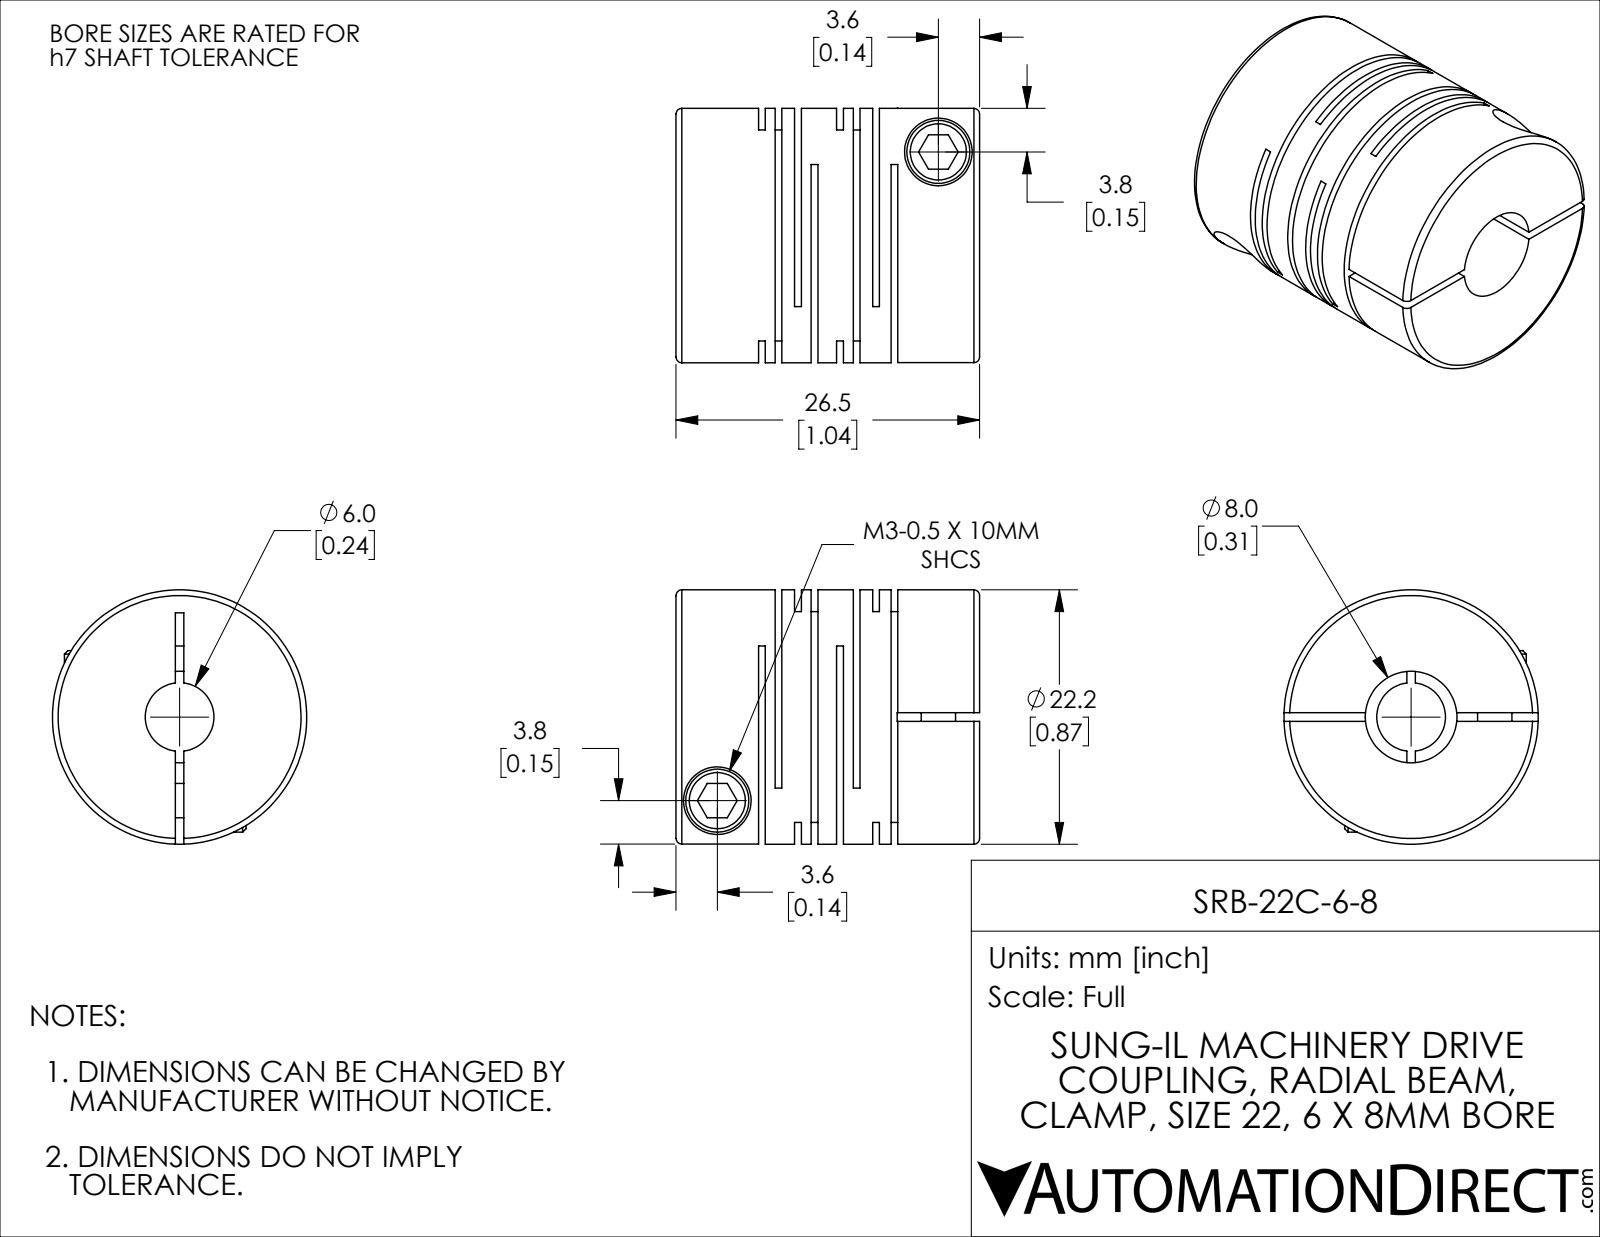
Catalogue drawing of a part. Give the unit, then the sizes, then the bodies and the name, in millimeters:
Units: millimetres
Overall size (bounding box): 26.5 × 22.2 × 22.2
Round holes (diameter × count): ⌀3 ×2, ⌀5.9 ×2, ⌀6 ×1, ⌀8 ×1
Round bosses / shafts (diameter × count): ⌀5.5 ×2, ⌀22.2 ×1
Main face-to-face distances: 0.59, 6.82, 1.45, 3.15, 5.37, 1.7, 3.67, 2.04, 7.41, 6.23
Volume: 7 458 mm³ · Surface area: 7 884 mm²
Bodies: 1 solid, 115 faces (60 planar, 42 cylindrical, 13 other)
Part name (STEP PRODUCT): SRB-22C-6-8
STEP written by: SolidWorks 2021 (CONFIG_CONTROL_DESIGN)
